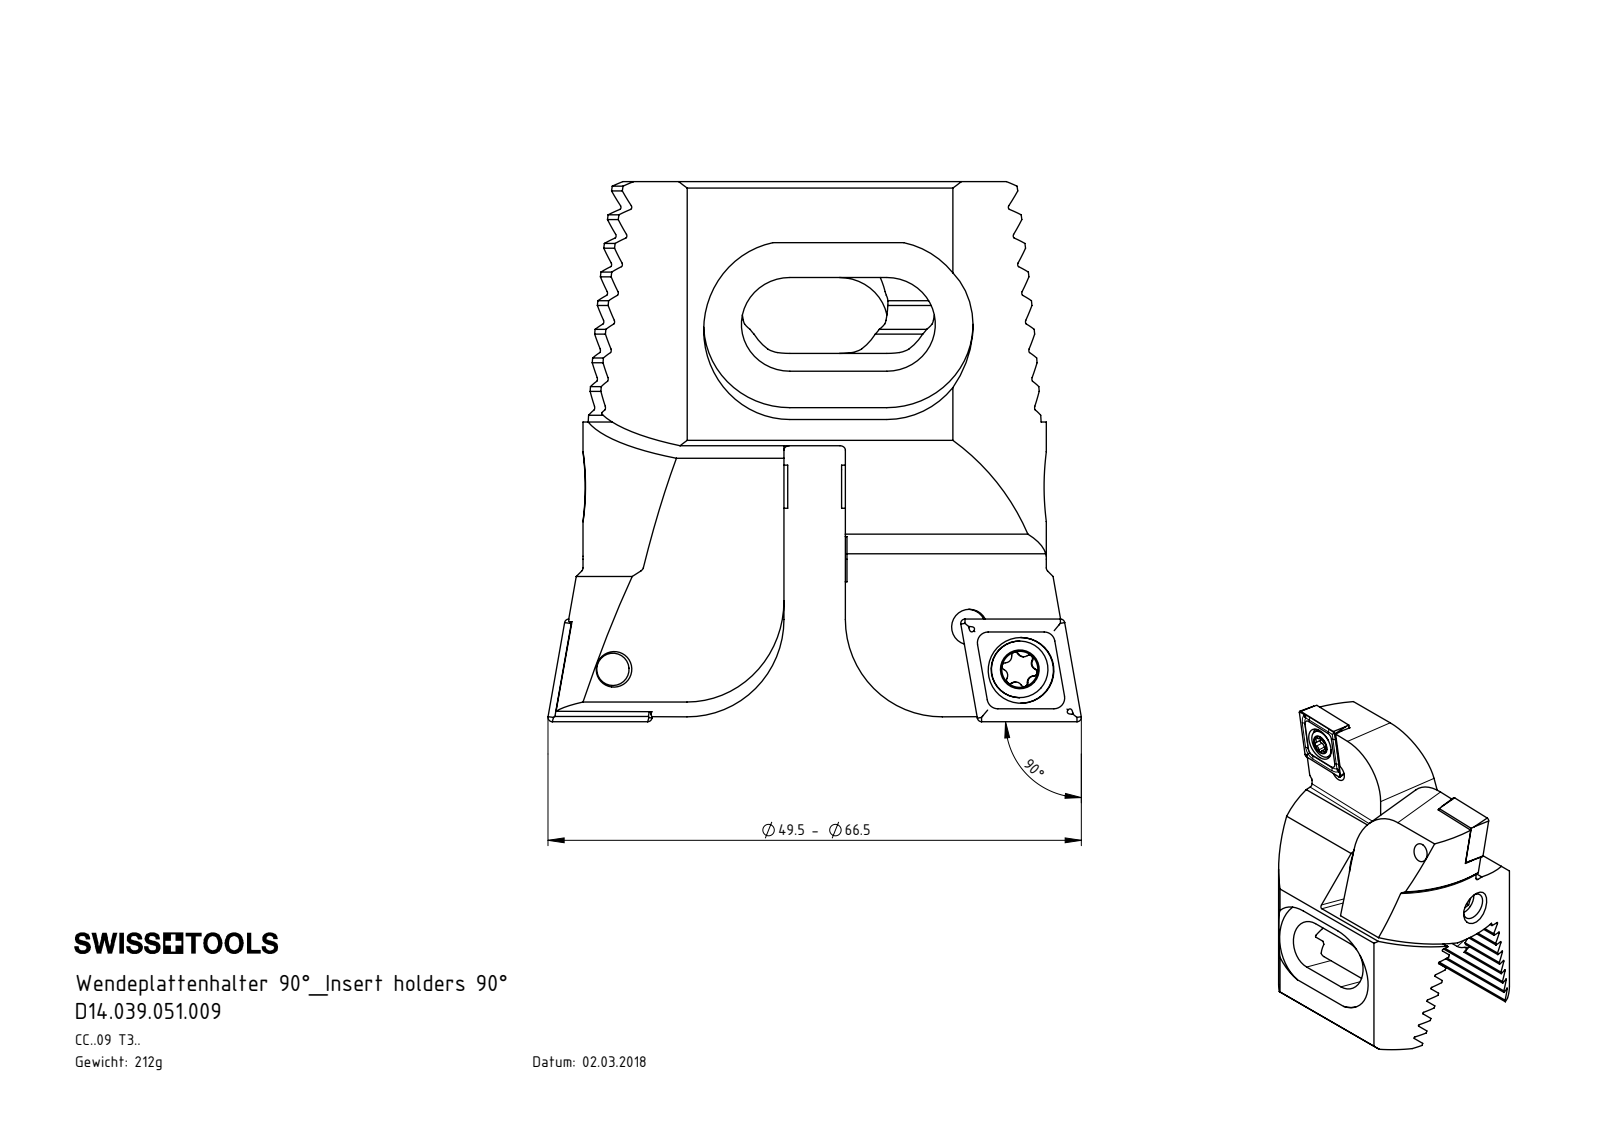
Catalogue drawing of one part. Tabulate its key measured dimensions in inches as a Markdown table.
| quantity | value |
| --- | --- |
| part name | D14.039.051.009; WCB-ER2.001.009_A; CCMT09T304; Z42-ER3.001.016 (+1 more) |
| STEP written by | SolidWorks 2015 (AUTOMOTIVE_DESIGN) |
| units | inches |
| bodies | 8 solids, 636 faces (326 planar, 126 cylindrical, 184 other) |
| overall size | 1.972 × 1.969 × 1.346 |
| volume | 1.667 in³ |
| surface area | 20.92 in² |
| round holes (diameter × count) | 0.13 × 4, 0.063 × 2, 0.173 × 2, 0.24 × 2, 0.197 × 1 |
| round bosses / shafts (diameter × count) | 0.157 × 3, 0.207 × 2, 0.236 × 1 |
| partial cylindrical surfaces (radius × count) | 0.008 × 16, 0.013 × 12, 0.023 × 12, 0.079 × 4, 0.177 × 4, 0.305 × 4, 0.472 × 4, 0.827 × 4 |
| main face-to-face distances | 0.094, 0.187, 0.469, 0.375, 0.563, 0.281, 0.188, 0.281, 0.063, 0.228 |
| hole center spacings | 0.239, 0.244, 0.472, 1.344, 1.348, 1.522, 0.913, 1.153 |
